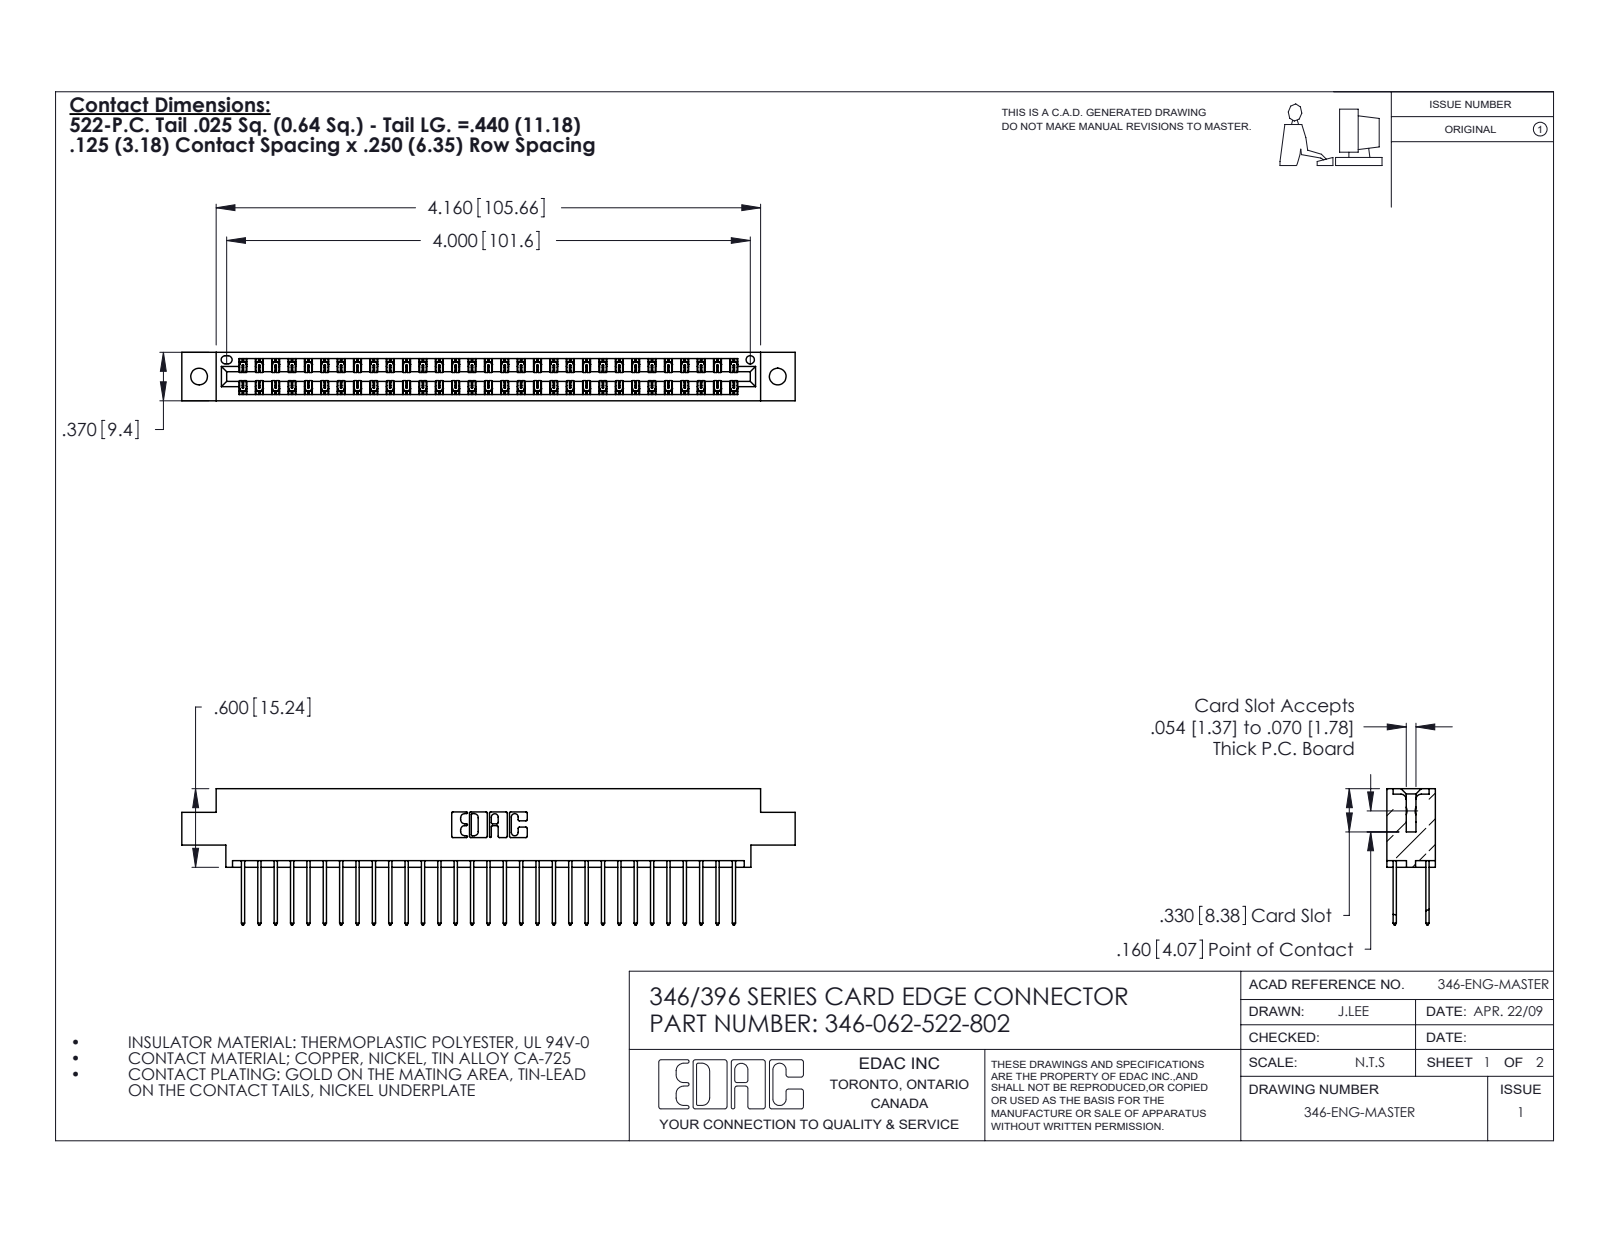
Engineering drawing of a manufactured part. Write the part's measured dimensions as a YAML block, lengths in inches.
part_name: "345-292-001_345-293-122; 346 Part_0.170 Offset - 0.128 Dia; 346-062-522-802"
step_written_by: "SolidWorks 2020 (CONFIG_CONTROL_DESIGN)"
units: inches
bodies: {solids: 63, faces: 3350, planar: 2250, cylindrical: 1100, other: 0}
overall_size: [4.685, 1.04, 0.37]
volume: 0.701
surface_area: 25.21
round_holes:
  - {diameter: 0.128, count: 2}
  - {diameter: 0.064, count: 1}
partial_cylinders:
  - {radius: 0.006, count: 93}
  - {radius: 0.01, count: 62}
  - {radius: 0.01, count: 22}
  - {radius: 0.007, count: 6}
  - {radius: 0.031, count: 6}
  - {radius: 0.026, count: 3}
  - {radius: 0.014, count: 2}
  - {radius: 0.022, count: 2}
face_to_face_distances: [0.048, 0.322, 0.25, 0.37, 0.072, 0.298, 0.025, 0.275, 0.148, 0.222]
hole_center_spacings: [0.246, 4.212, 4.42]
